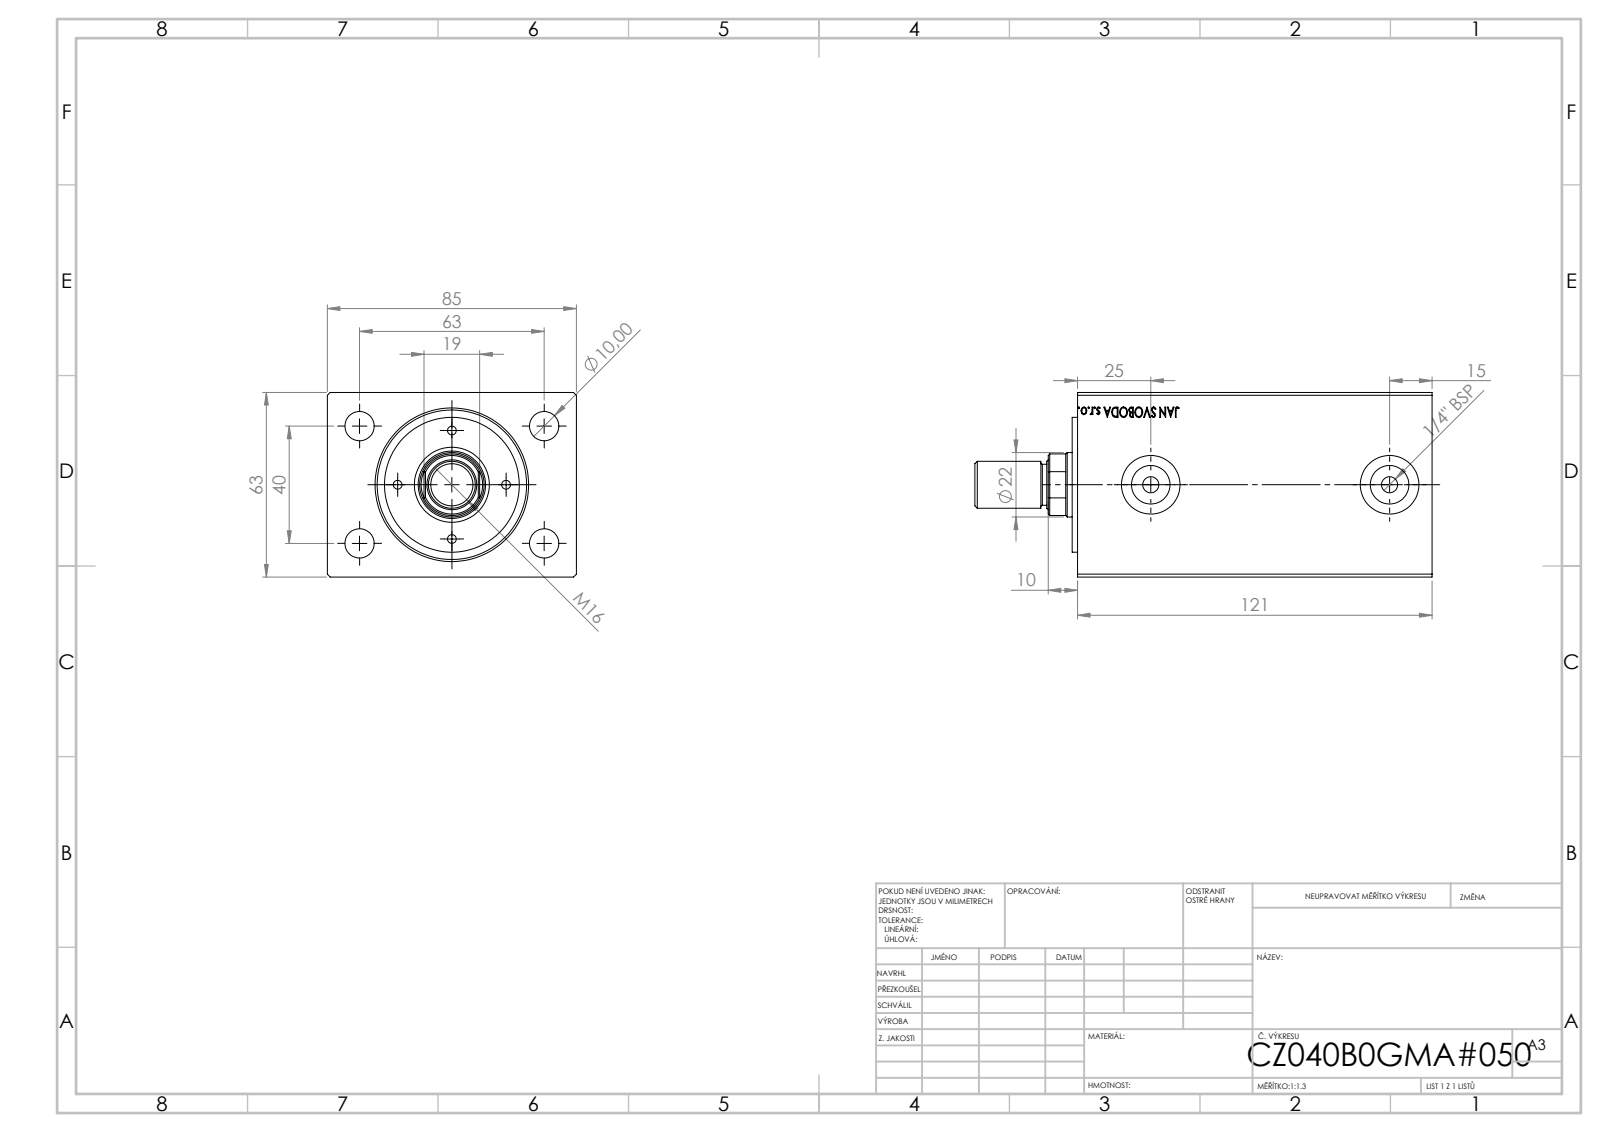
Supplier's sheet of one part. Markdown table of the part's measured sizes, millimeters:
| quantity | value |
| --- | --- |
| part name | V500CZ_MALE_METRIC; V500CZ; V500CZ_B_VC |
| STEP written by | SolidWorks 2019 (CONFIG_CONTROL_DESIGN) |
| units | millimeters |
| bodies | 4 solids, 887 faces (403 planar, 62 cylindrical, 422 other) |
| overall size | 156 × 85 × 63 |
| volume | 628 399 mm³ |
| surface area | 104 552 mm² |
| round holes (diameter × count) | 3 × 4, 10 × 4, 5.5 × 2, 13.16 × 2, 20 × 2, 14.5 × 1, 22 × 1, 23 × 1, 36 × 1, 40 × 1, 51 × 1 |
| round bosses / shafts (diameter × count) | 46 × 1, 16 × 1, 14 × 1 |
| partial cylindrical surfaces (radius × count) | 10.5 × 1 |
| main face-to-face distances | 63, 85, 121, 106.3, 14.7, 71, 35.3, 50, 1.8, 72.8 |
| hole center spacings | 18.5, 23.85, 26.16, 31.54, 37.31, 49.74, 53.85, 37 |
